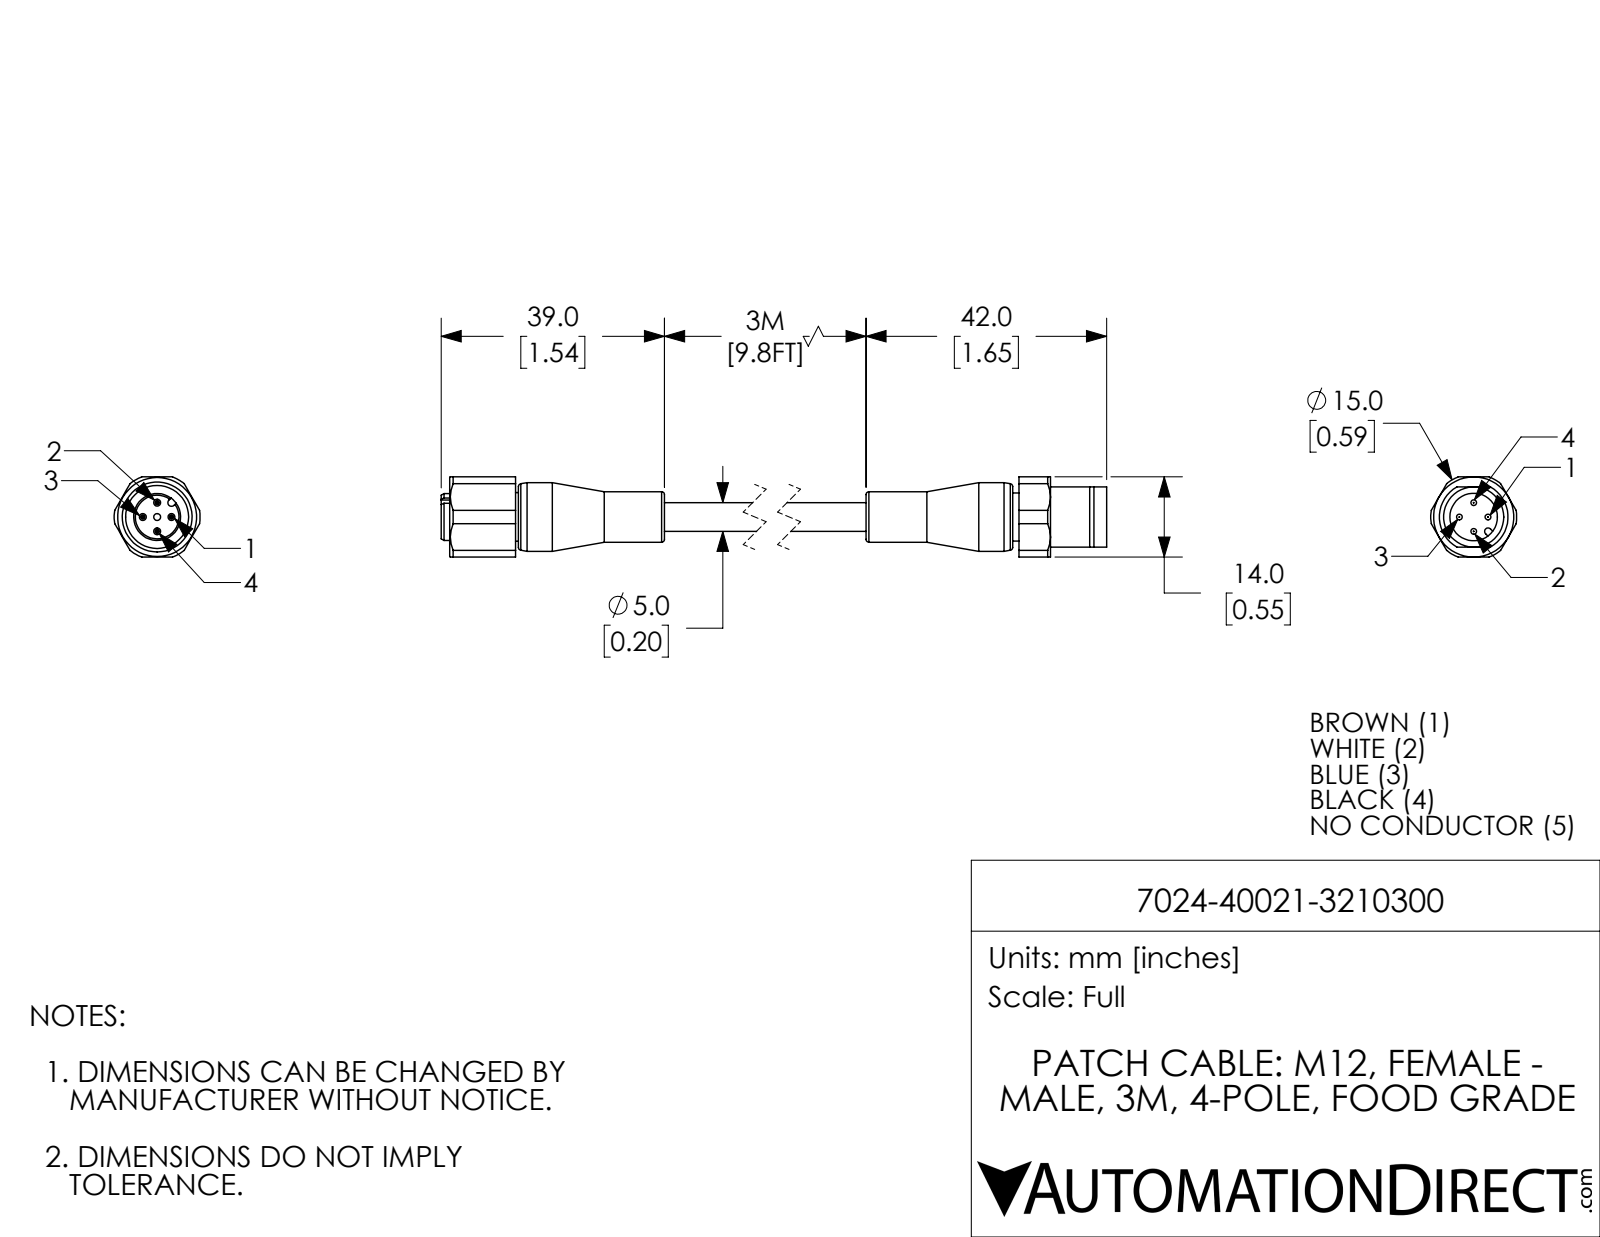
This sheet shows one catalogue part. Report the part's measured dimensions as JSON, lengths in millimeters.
{"part_name": "7024-40021-3210300_MALE; 7024-40021-3210300; 7024-40021-3210300_FEMALE", "step_written_by": "SolidWorks 2018 (AUTOMOTIVE_DESIGN)", "units": "millimeters", "bodies": {"solids": 2, "faces": 144, "planar": 43, "cylindrical": 60, "other": 41}, "overall_size": [131.2, 15, 14], "volume_mm3": 8050, "surface_area_mm2": 5071, "round_holes": [[1.2, 5], [8.3, 1], [11, 1]], "round_bosses_or_shafts": [[1, 4], [12, 1], [10.5, 1], [8.8, 1], [8.5, 1], [8.4, 1], [8.2, 1], [5, 1]], "partial_cylinders_radius": [[0.6, 1], [0.7, 1], [7.5, 1]], "face_to_face_distances": [14, 102.9, 1.8, 12.2, 113.3, 7.5, 5.5, 109.3, 6.4, 108.4], "hole_center_spacings": [2.5, 3.5, 5]}
